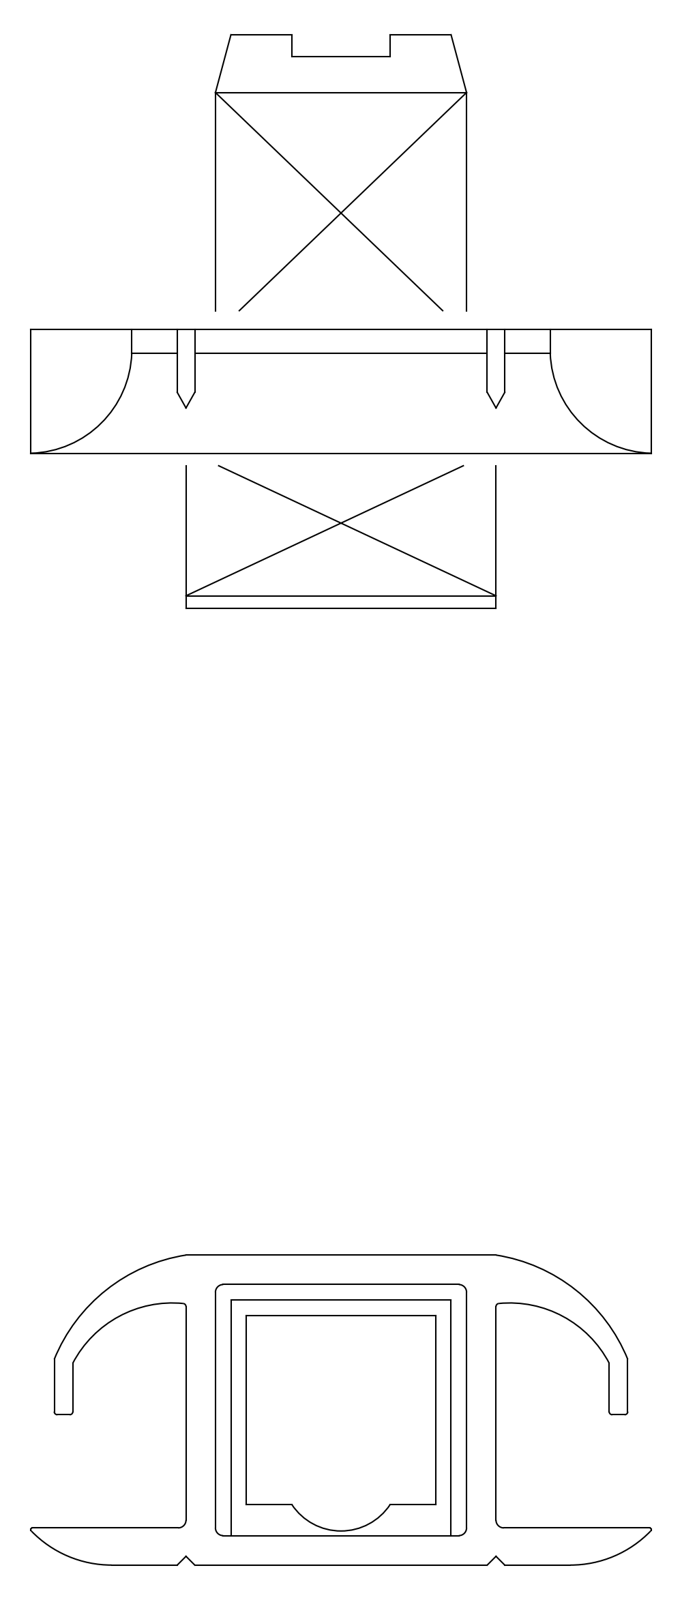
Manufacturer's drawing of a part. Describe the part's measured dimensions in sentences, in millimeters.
Its 3-D file was written by "THINKDESIGN (CONFIG_CONTROL_DESIGN)". It is 1 solid with 73 faces: 46 planar, 18 cylindrical and 9 other. Overall it measures 40.33 by 37 by 20 millimeters. Its volume is 6 874 cubic millimeters and its surface area 5 685 square millimeters. Round holes: 1 of diameter 3.75. Partial cylindrical surfaces (rounded edges, fillets, slot ends): 6 of radius 0.5, 3 of radius 7.2, 3 of radius 11, 2 of radius 3, 2 of radius 7.24, 1 of radius 3.8. The main face-to-face distances are 2, 14.2, 3.9, 1.9, 18.1, 16.1, 16.2, 12.2, 17.6, 13.7.
